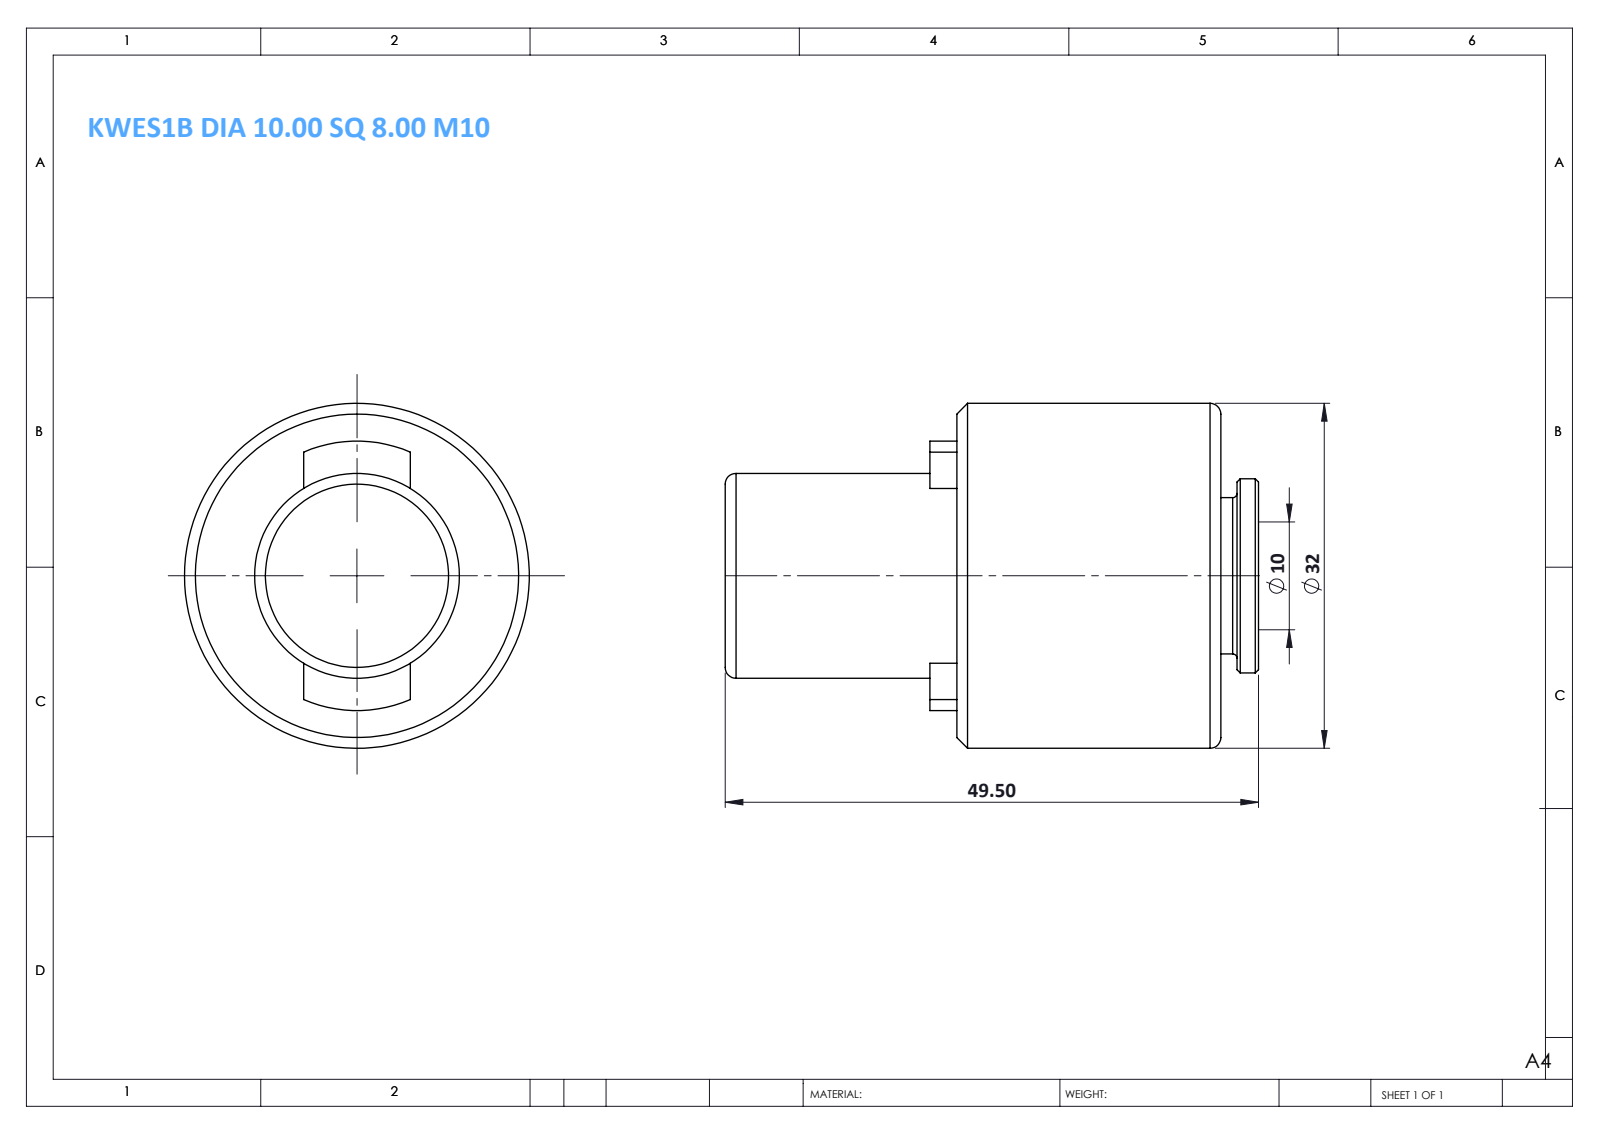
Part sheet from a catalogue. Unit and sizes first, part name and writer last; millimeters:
Units: millimetres
Overall size (bounding box): 49.5 × 32 × 32
Round holes (diameter × count): ⌀10 ×1
Round bosses / shafts (diameter × count): ⌀32 ×1, ⌀19 ×1, ⌀18 ×1, ⌀14.5 ×1
Partial cylindrical surfaces — rounded edges, fillets, slot ends (radius × count): R12.5 ×1
Main face-to-face distances: 24.5, 21.5, 46, 14, 49.5, 28, 3.5, 35.5, 10.5, 19
Volume: 25 521 mm³ · Surface area: 6 021 mm²
Bodies: 1 solid, 39 faces (12 planar, 13 cylindrical, 14 other)
Part name (STEP PRODUCT): KWES1B DIA 10.00 SQ 8.00 M10
STEP written by: SolidWorks 2014 (CONFIG_CONTROL_DESIGN)
